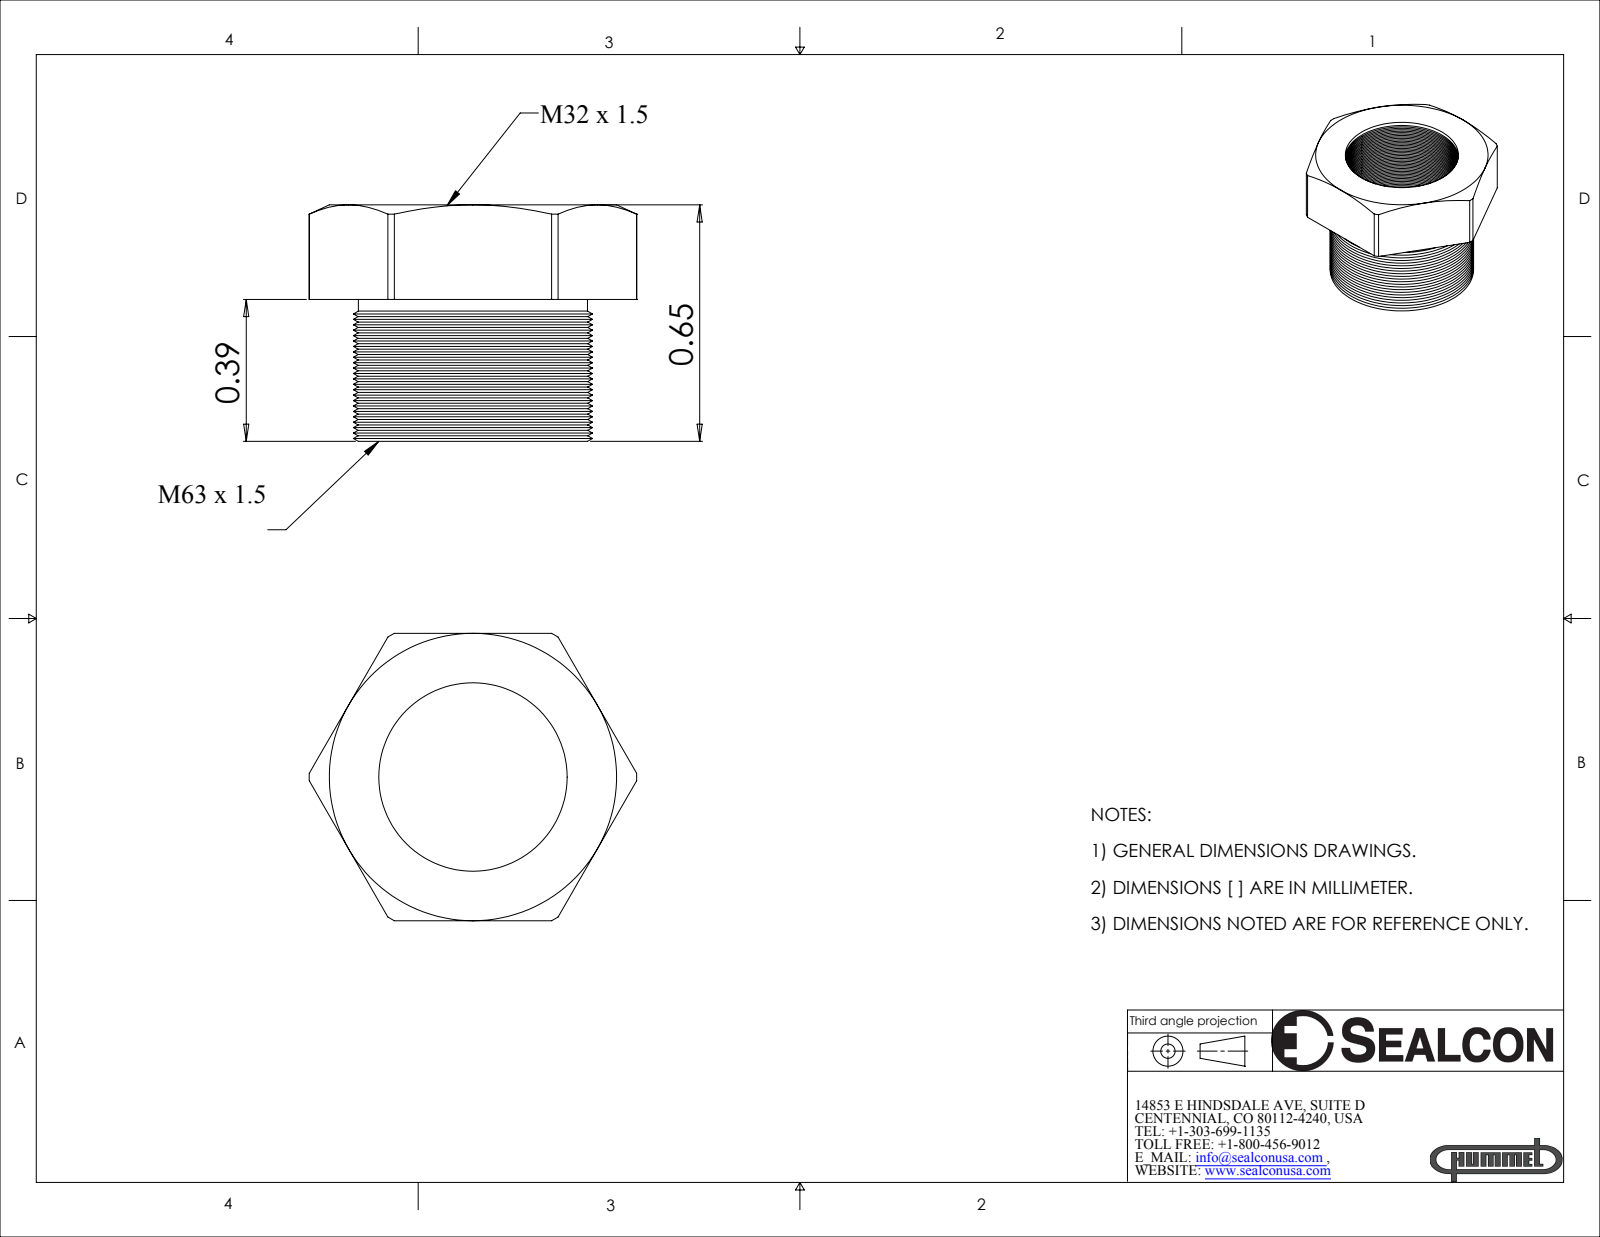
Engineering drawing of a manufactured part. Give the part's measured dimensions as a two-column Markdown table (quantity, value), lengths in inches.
| quantity | value |
| --- | --- |
| part name | RM-6332-SS |
| STEP written by | SolidWorks 2008 (CONFIG_CONTROL_DESIGN) |
| units | inches |
| bodies | 1 solid, 363 faces (9 planar, 91 cylindrical, 263 other) |
| overall size | 0.901 × 0.79 × 0.65 |
| volume | 0.127 in³ |
| surface area | 4.999 in² |
| round holes (diameter × count) | 0.518 × 1, 0.63 × 1 |
| partial cylindrical surfaces (radius × count) | 0.45 × 1 |
| main face-to-face distances | 0.79, 0.26, 0.39, 0.65 |
